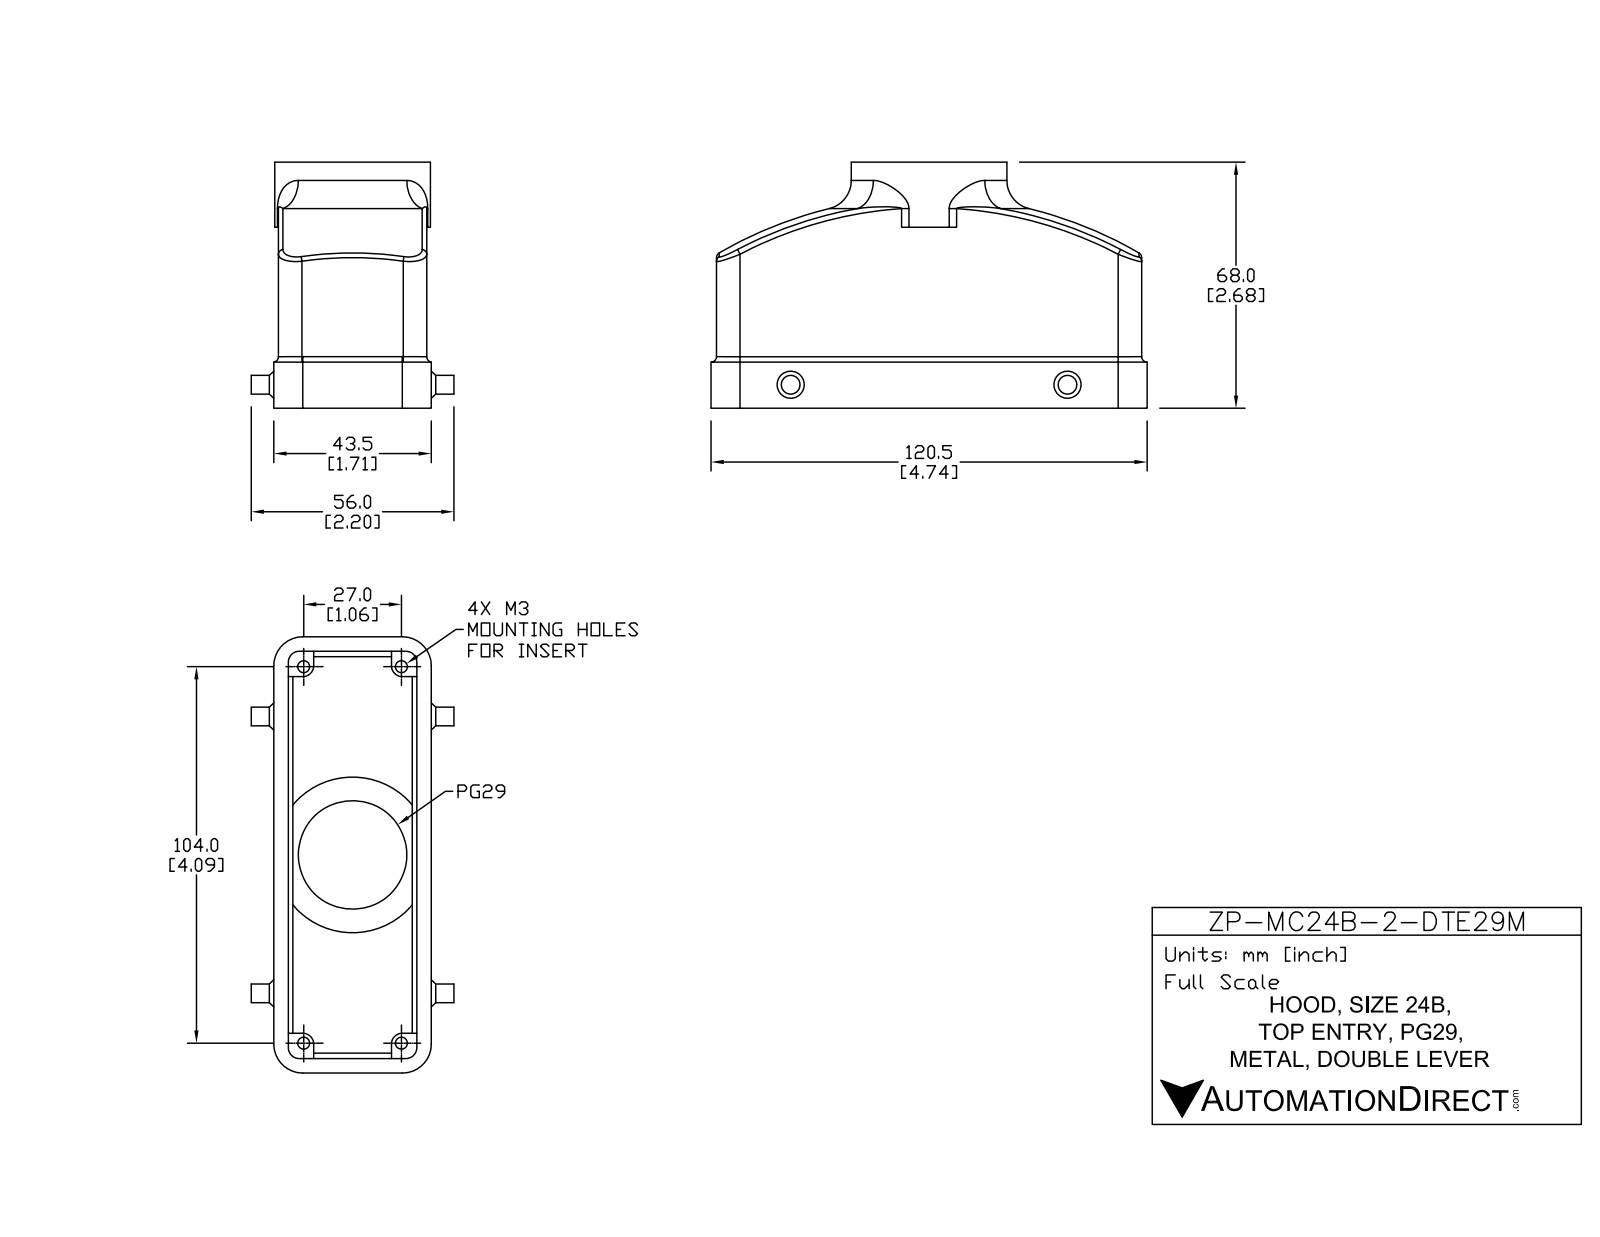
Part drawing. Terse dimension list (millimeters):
name: ZP-MC24B-2-DTE29M
written by: SolidWorks 2011 (AUTOMOTIVE_DESIGN)
unit: mm
bodies: 5 solids, 119 faces (46 planar, 41 cylindrical, 32 other)
size: 120.5 × 68 × 56
volume: 83 215 mm³; area: 41 730 mm²
holes: 4× ⌀3.3, 1× ⌀30, 1× ⌀35
bosses: 2× ⌀5.17, 1× ⌀43
rounds: 8× R3, 8× R8, 4× R1.5, 4× R5.5, 4× R6.5
face distances: 4, 37, 1.25, 38.25, 41, 33, 5.25, 42.25, 39.5, 2.75
hole spacings: 53.72, 27, 104, 107.45
